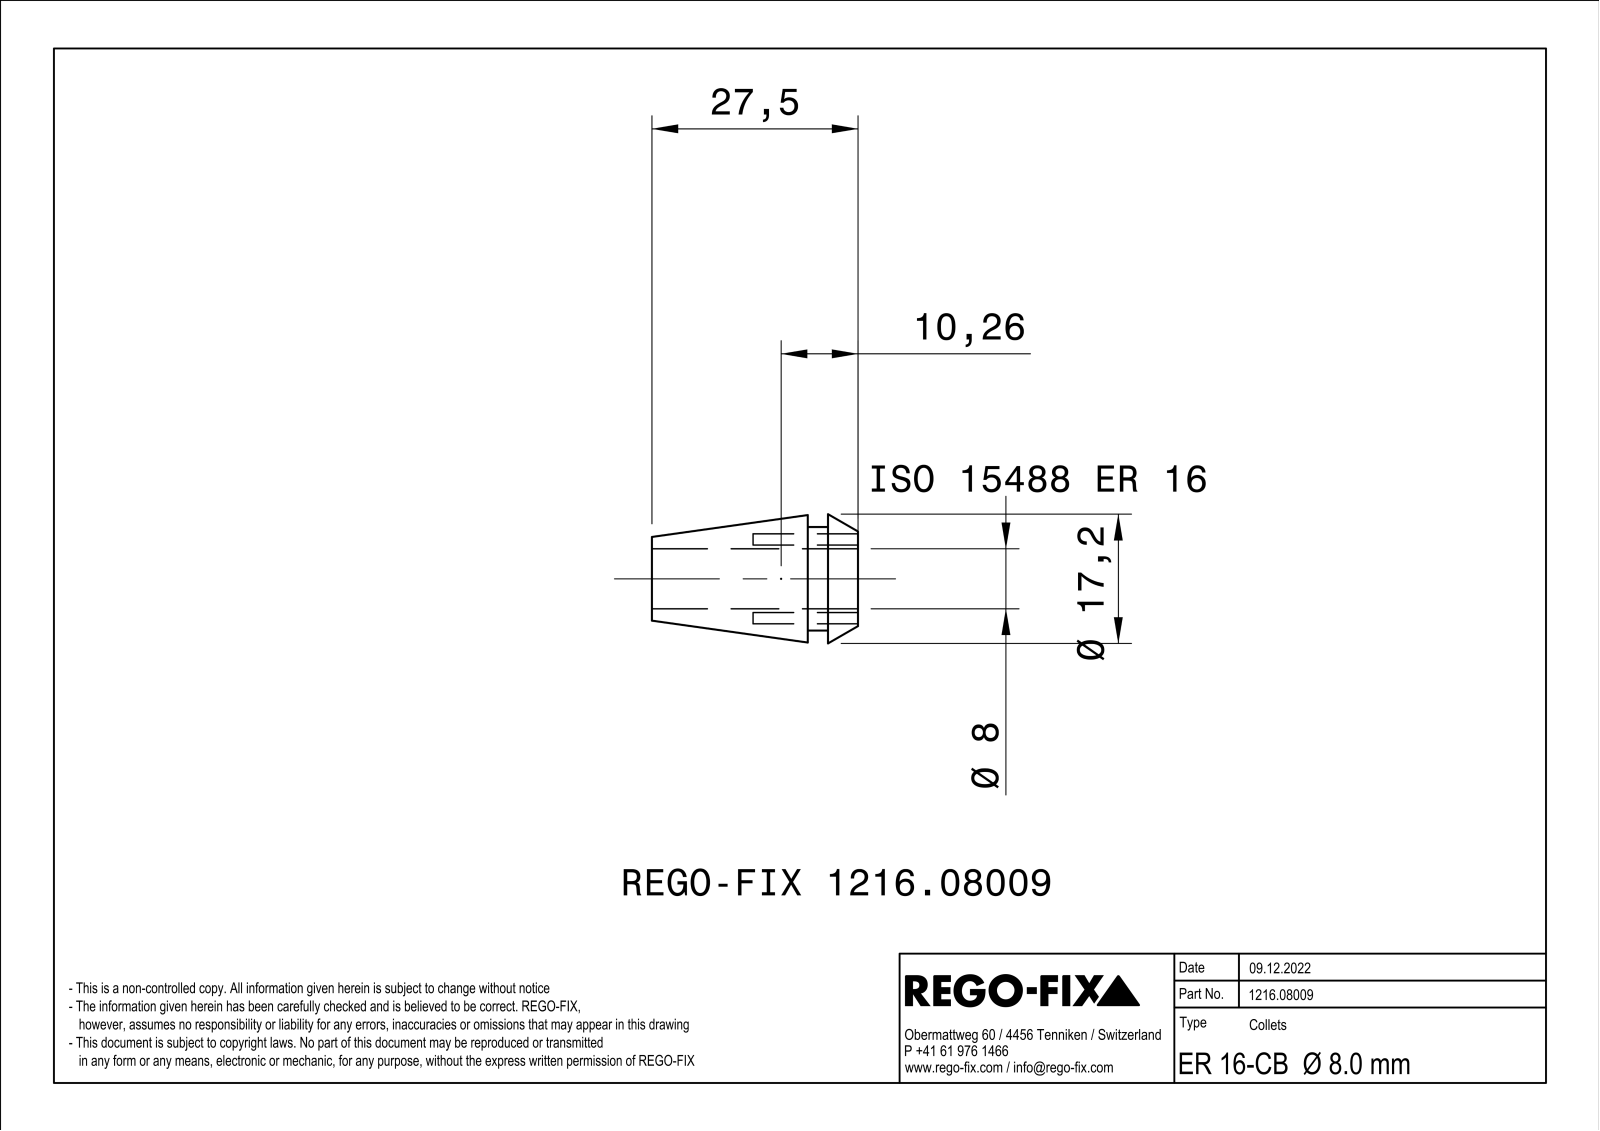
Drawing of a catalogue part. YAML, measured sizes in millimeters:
part_name: "NOCUT"
step_written_by: "SIEMENS PLM Software Solid Edge ST10 (AUTOMOTIVE_DESIGN)"
units: millimeters
bodies: {solids: 1, faces: 178, planar: 64, cylindrical: 21, other: 93}
overall_size: [27.5, 16.99, 16.99]
volume: 2361
surface_area: 3872
round_holes:
  - {diameter: 1.5, count: 4}
  - {diameter: 8, count: 1}
round_bosses_or_shafts:
  - {diameter: 17, count: 1}
  - {diameter: 13.8, count: 1}
face_to_face_distances: [0.6, 4, 6.7, 2.7, 27.5, 23.5, 20.8]
hole_center_spacings: [5.25, 7.42, 10.5]
